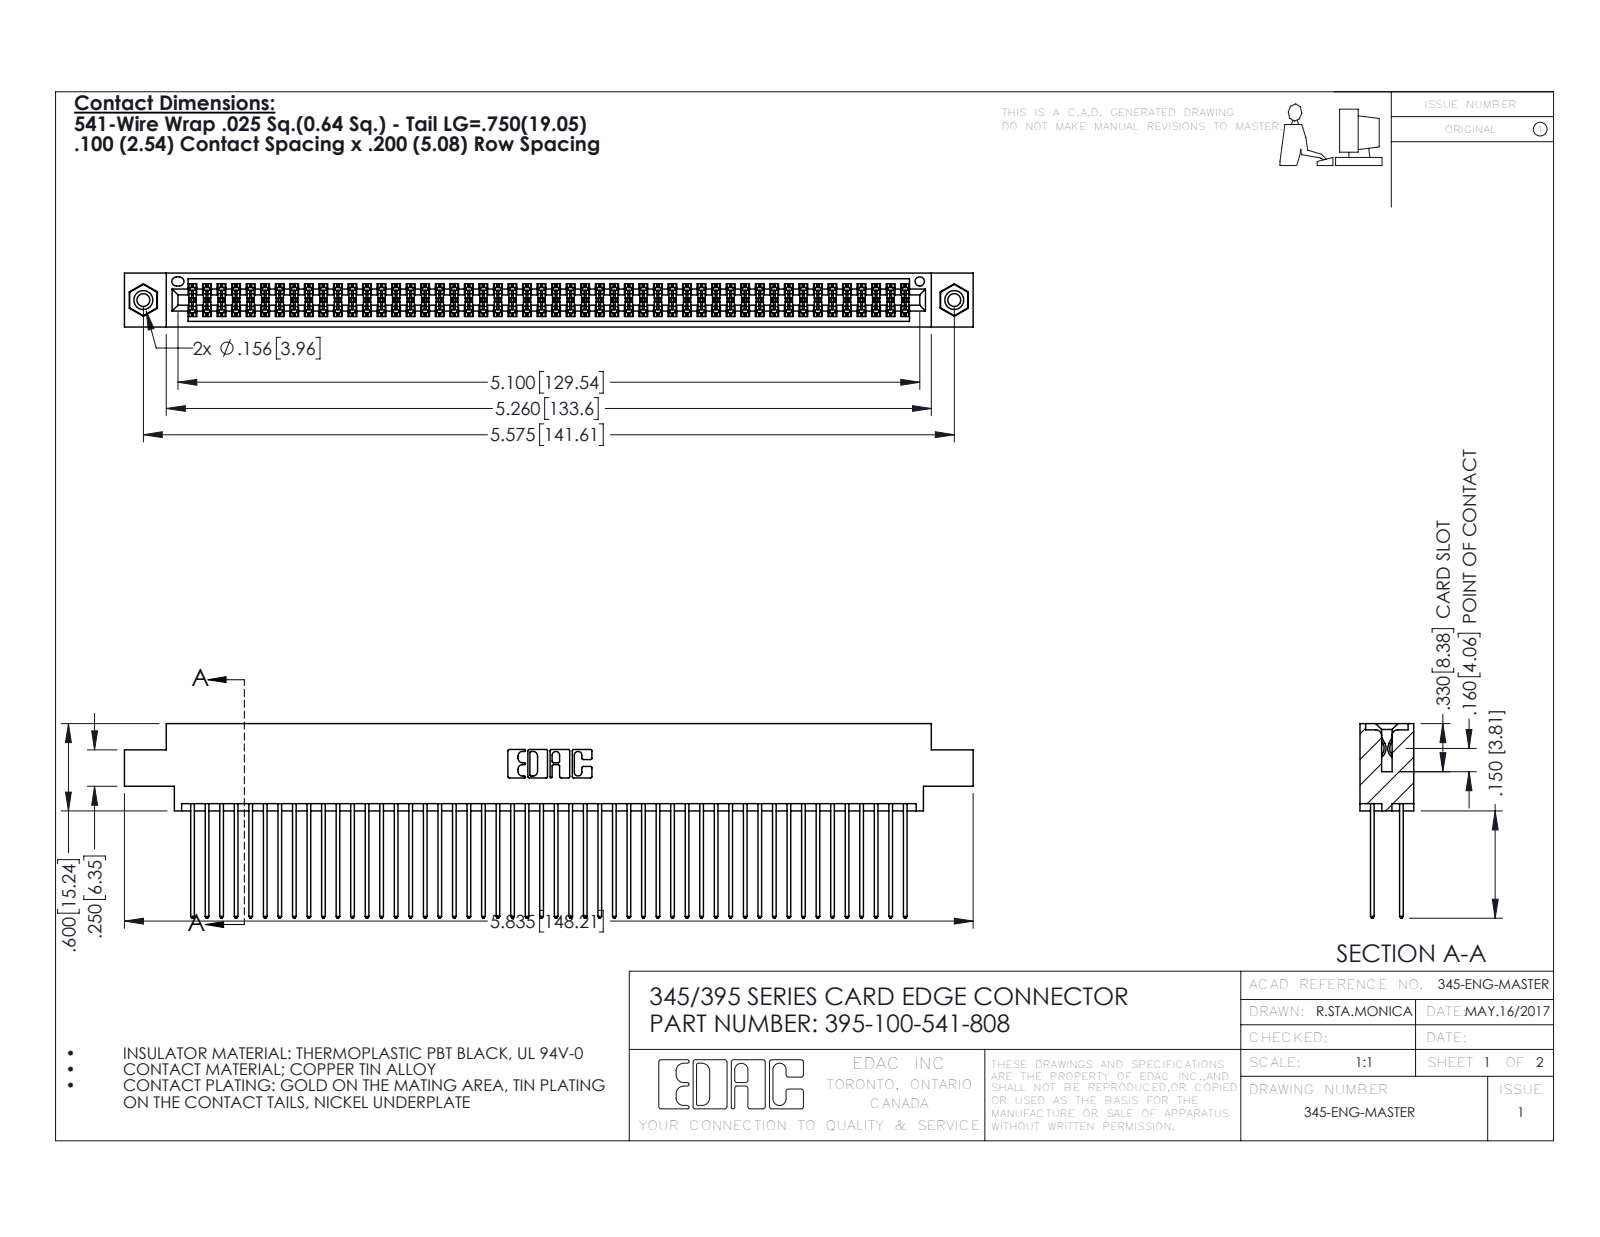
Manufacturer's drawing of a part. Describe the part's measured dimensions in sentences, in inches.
The part is named "345-292-001_345-293-141; 345 Part_0.170 Offset - 0.156 Dia-TI; 345-250-001_345-250-003-102; 395-100-541-808". Its 3-D file was written by "SolidWorks 2016 (CONFIG_CONTROL_DESIGN)". It is 103 solids with 5190 faces: 3416 planar, 1758 cylindrical and 16 other. Overall it measures 5.835 by 1.337 by 0.37 inches. Its volume is 0.911 cubic inches and its surface area 38.86 square inches. Round holes: 2 of diameter 0.089, 2 of diameter 0.125, 2 of diameter 0.156, 1 of diameter 0.064. Round bosses or shafts: 2 of diameter 0.155. Partial cylindrical surfaces (rounded edges, fillets, slot ends): 150 of radius 0.006, 100 of radius 0.01, 22 of radius 0.01, 6 of radius 0.007, 6 of radius 0.031, 3 of radius 0.026, 2 of radius 0.014, 2 of radius 0.019. The main face-to-face distances are 0.072, 0.298, 0.2, 0.098, 0.272, 0.025, 0.225, 0.37, 0.175, 0.149. The hole center spacings are 0.27, 5.339, 5.575.
